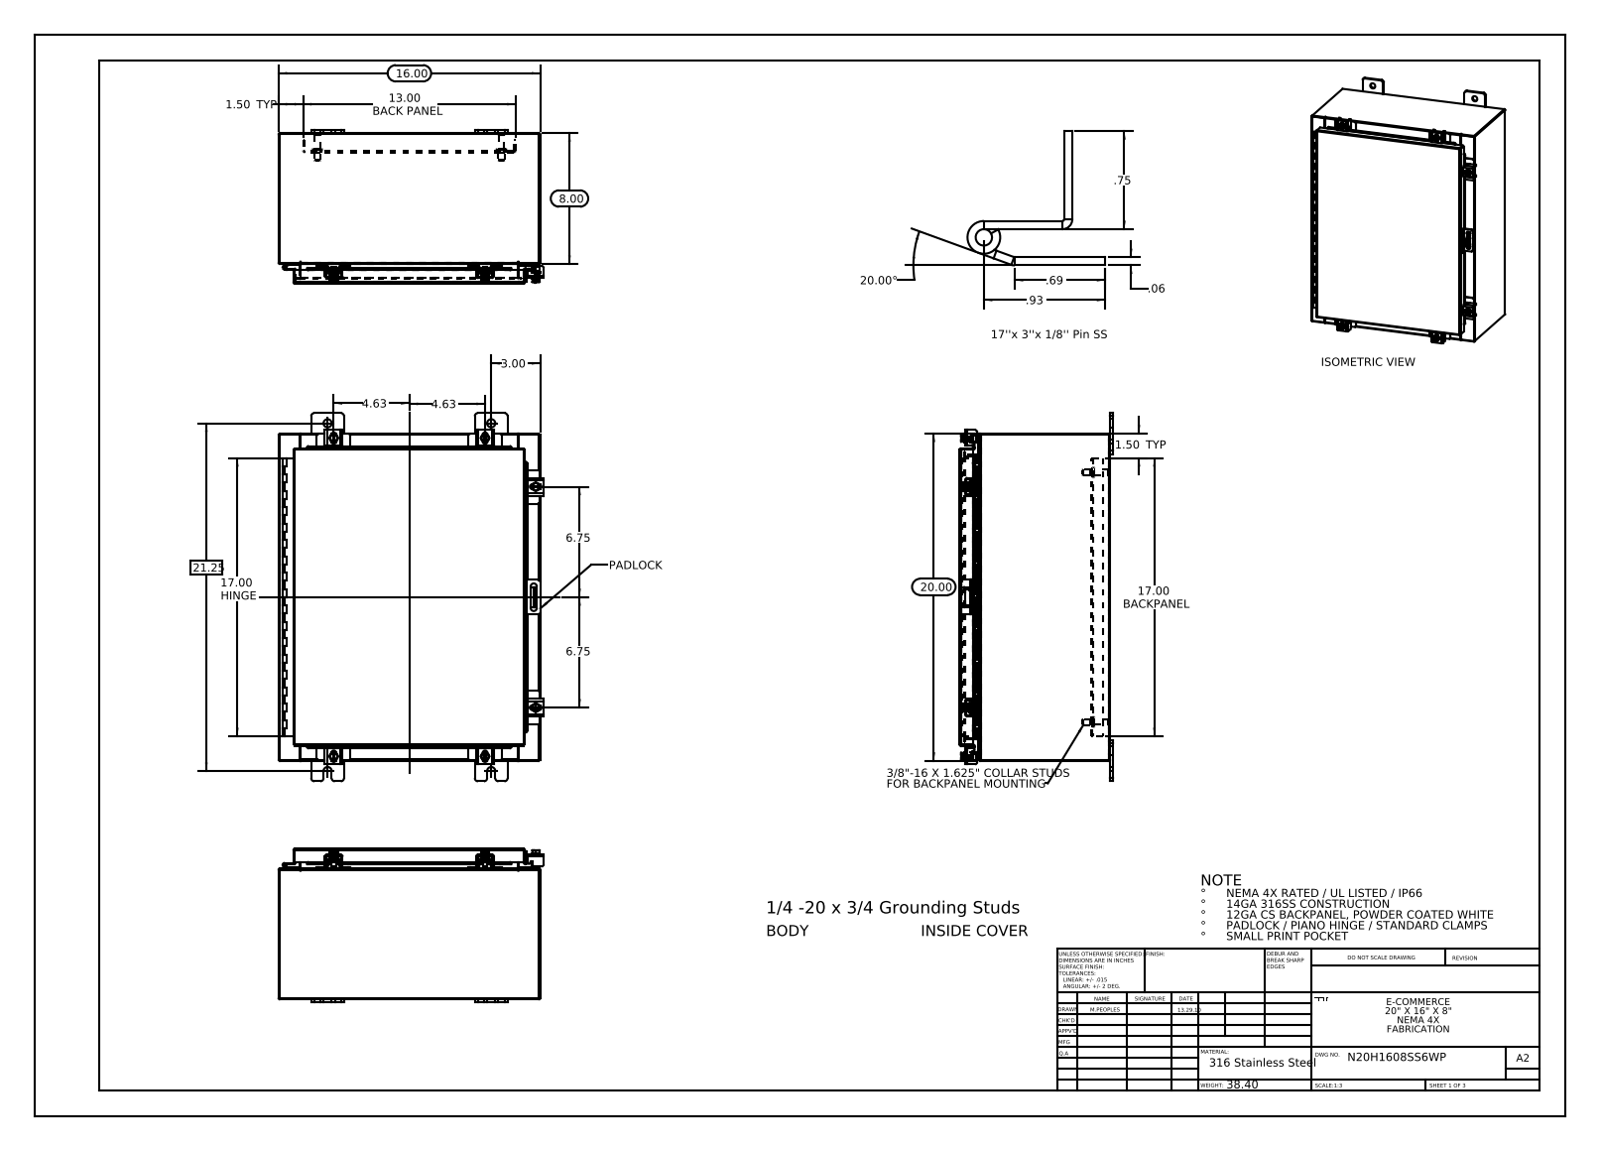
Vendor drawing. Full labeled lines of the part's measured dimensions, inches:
Part name (STEP PRODUCT): N20H1608SS6WP Hinge Enclosure Side2; N20H1608SS6WP 22101002; N20H1608SS6WP Padlock Hasp; N20H1608SS6WP Clamp Top (+8 more)
STEP written by: SolidWorks 2013 (CONFIG_CONTROL_DESIGN)
Units: inches
Bodies: 47 solids, 1613 faces (860 planar, 657 cylindrical, 96 other)
Overall size (bounding box): 22.5 × 16.211 × 9.389
Volume: 135.6 in³ · Surface area: 3 435 in²
Round holes (diameter × count): ⌀0.5 ×8, ⌀0.213 ×6, ⌀0.26 ×6, ⌀0.125 ×2, ⌀0.125 ×1
Round bosses / shafts (diameter × count): ⌀0.25 ×7, ⌀0.5 ×6, ⌀0.399 ×6, ⌀0.625 ×4, ⌀0.375 ×4, ⌀0.33 ×4
Partial cylindrical surfaces — rounded edges, fillets, slot ends (radius × count): R0.06 ×30, R0.013 ×25, R0.19 ×24, R0.088 ×21, R0.12 ×12, R0.141 ×12, R0.125 ×10, R0.05 ×9
Main face-to-face distances: 0.075, 9.126, 15.925, 9.201, 9.051, 19.925, 0.104, 1, 1.075, 8.051
Hole centre spacings: 17.38, 1.858, 2.276, 2.326, 2.326, 3.065, 4.297, 9.25
